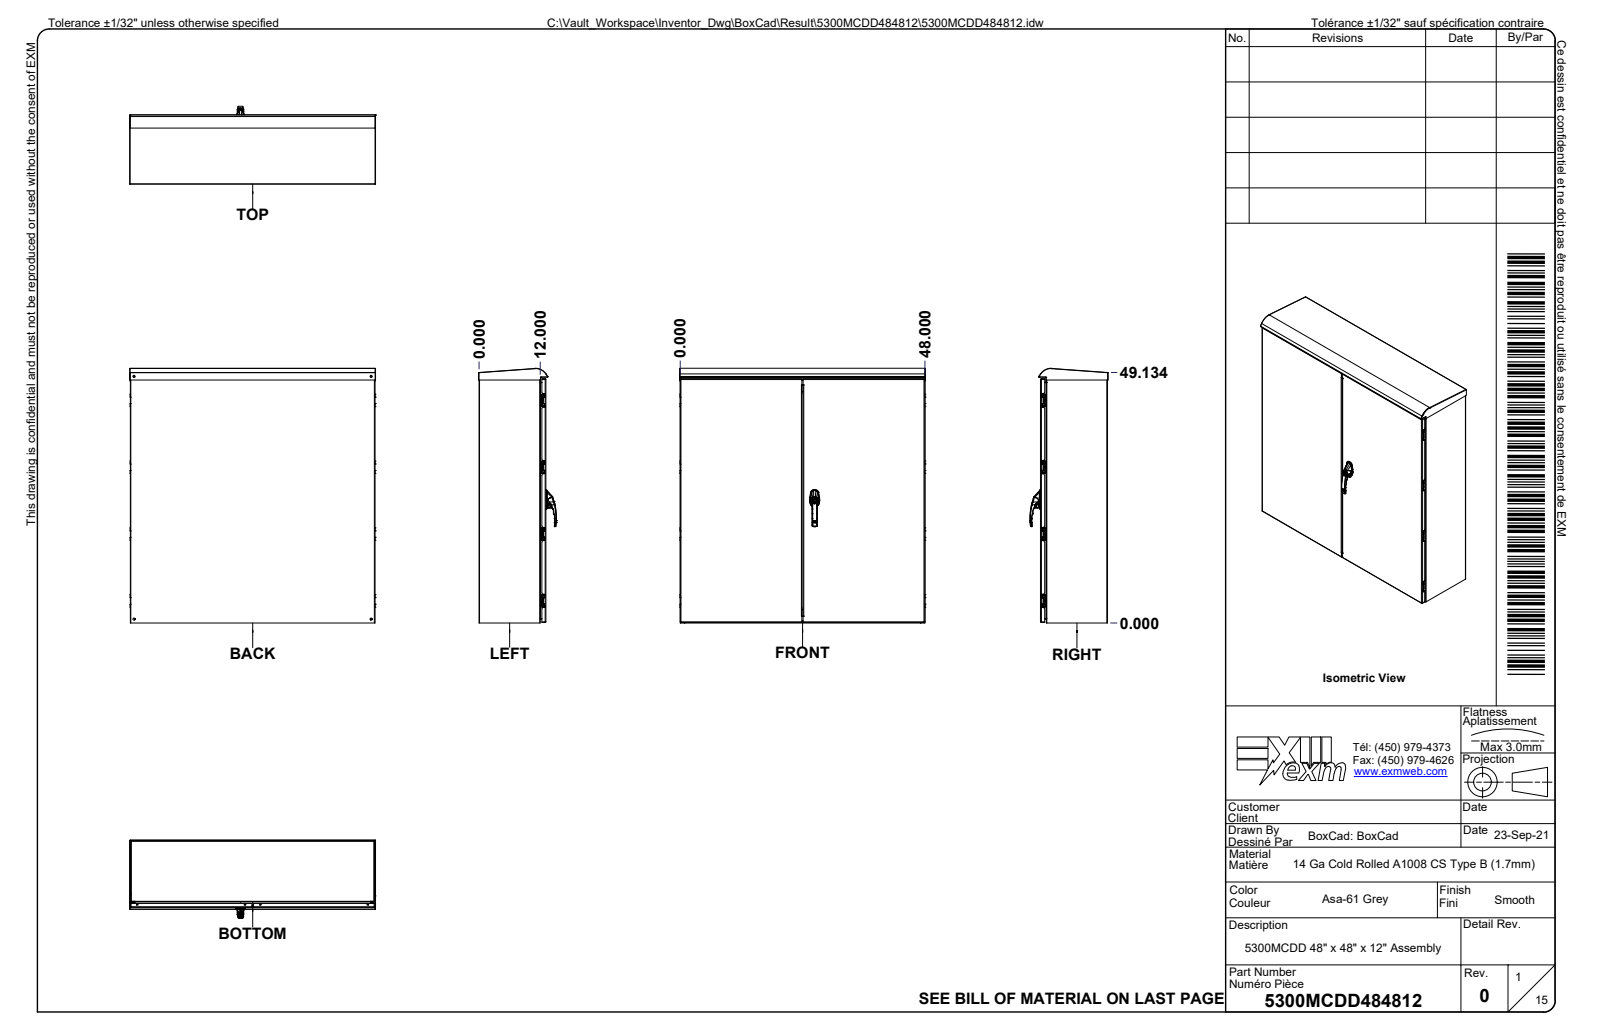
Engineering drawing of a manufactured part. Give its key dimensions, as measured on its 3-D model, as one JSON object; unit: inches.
{"part_name": "5300MCDD484812; 5300MCDD484812B; 5300MCDD484812B-P; 5300MCDD484812BT-P (+8 more)", "step_written_by": "Autodesk Inventor 2024 (AUTOMOTIVE_DESIGN)", "units": "inches", "bodies": {"solids": 142, "faces": 22504, "planar": 6831, "cylindrical": 5570, "other": 10103}, "overall_size": [49.932, 48.206, 15.3], "volume_in3": 700.5, "surface_area_in2": 20614, "round_holes": [[0.29, 26], [0.043, 24], [0.03, 14], [0.167, 10], [0.315, 10], [0.5, 10], [0.178, 8], [0.27, 8], [0.201, 6], [0.305, 6], [0.22, 4], [0.33, 4]], "round_bosses_or_shafts": [[0.039, 24], [0.03, 13], [0.717, 8], [0.311, 8], [0.262, 8], [0.232, 8], [0.472, 6], [0.3, 6]], "partial_cylinders_radius": [[0.02, 419], [0.01, 359], [0.039, 338], [0.008, 253], [0.016, 119], [0.004, 118], [0.079, 83], [0.031, 72]], "face_to_face_distances": [0.068, 13.052, 12.983, 13.12, 0.068, 0.874, 0.942, 12.109, 12.178, 1.01], "hole_center_spacings": [5.5, 48.265, 11, 49.196, 16.5, 47.95, 50.709, 13.101]}
